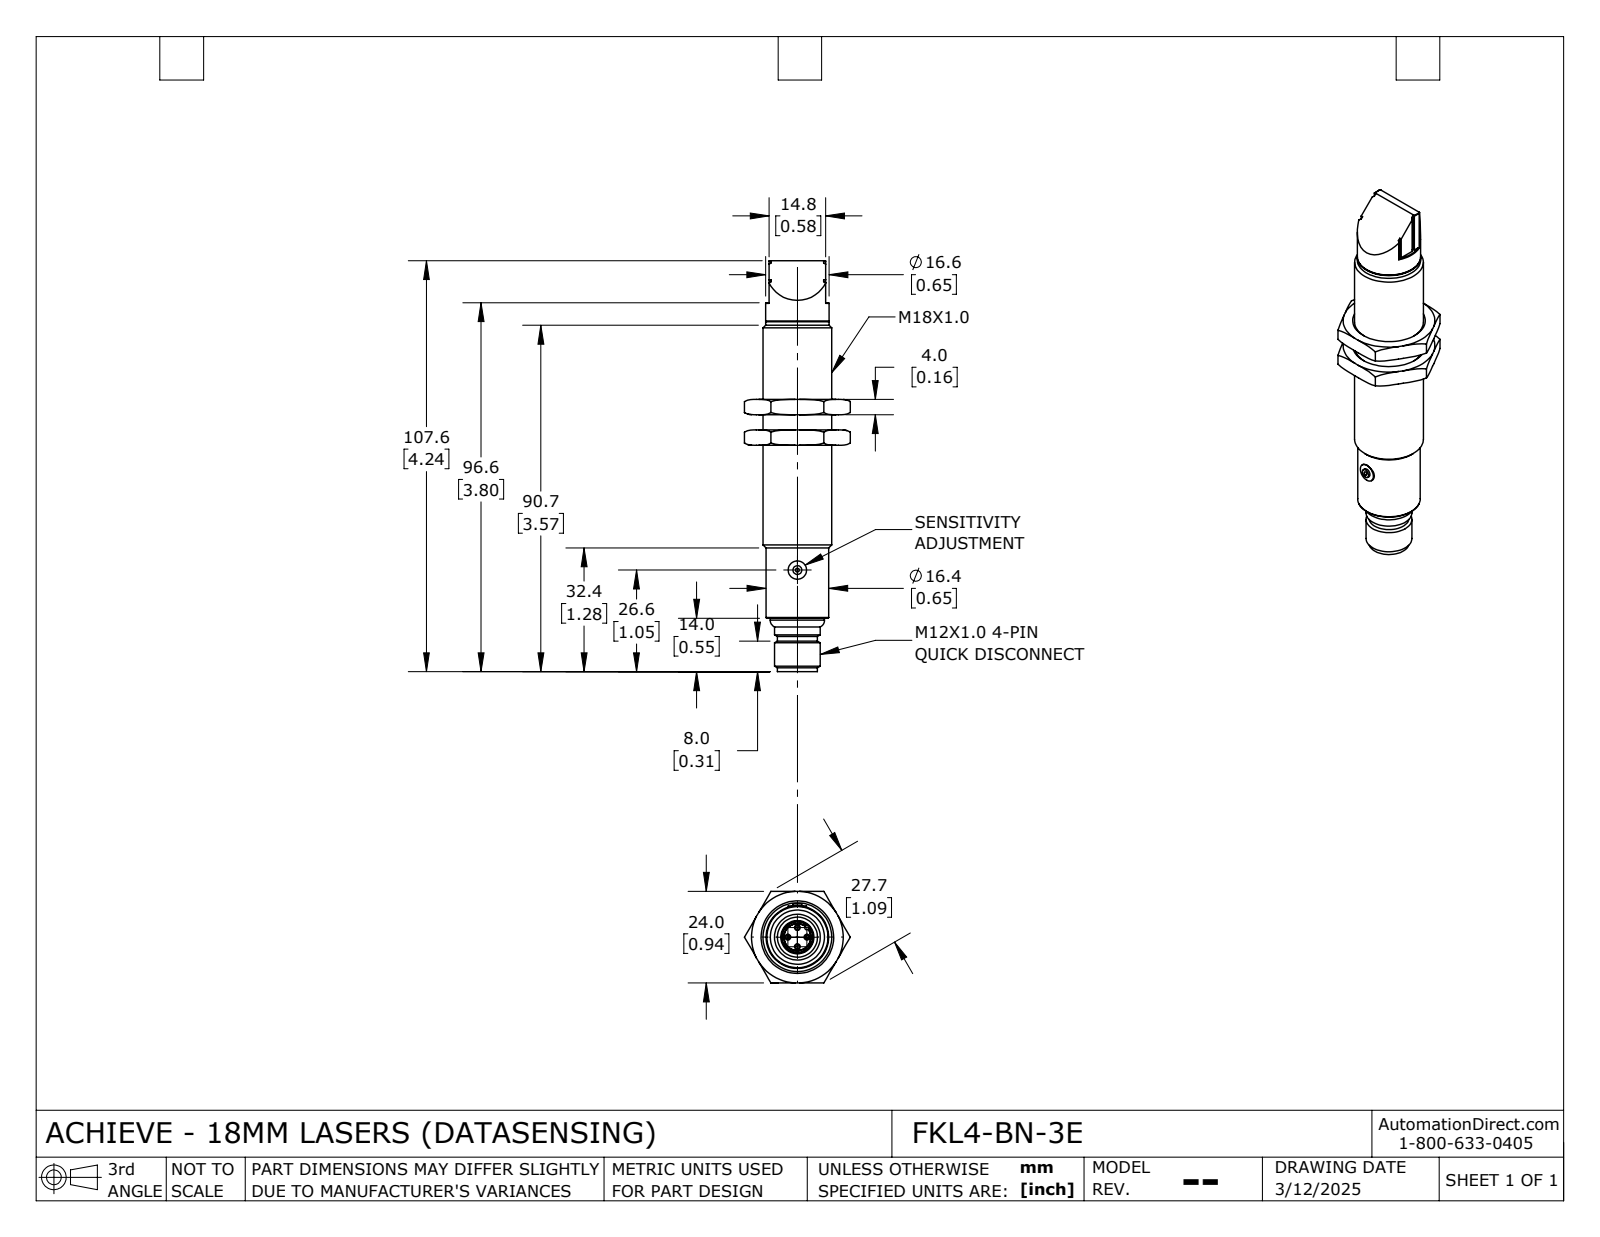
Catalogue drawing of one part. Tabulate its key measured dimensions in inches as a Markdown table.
| quantity | value |
| --- | --- |
| part name | FKL4-BN-3E_Default |
| STEP written by | SolidWorks 2024 (CONFIG_CONTROL_DESIGN) |
| units | inches |
| bodies | 3 solids, 146 faces (64 planar, 30 cylindrical, 52 other) |
| overall size | 4.236 × 1.091 × 0.945 |
| volume | 1.472 in³ |
| surface area | 14.05 in² |
| round holes (diameter × count) | 0.185 × 1, 0.278 × 1, 0.327 × 1, 0.583 × 1, 0.709 × 1 |
| round bosses / shafts (diameter × count) | 0.039 × 4, 0.654 × 1, 0.646 × 1, 0.559 × 1, 0.472 × 1, 0.413 × 1, 0.276 × 1, 0.189 × 1 |
| partial cylindrical surfaces (radius × count) | 0.004 × 2, 0.02 × 2, 0.024 × 1, 0.297 × 1 |
| main face-to-face distances | 0.157, 0.315, 0.945, 1.253, 1.261, 0.938, 0.946, 0.472, 1.41, 1.418 |
